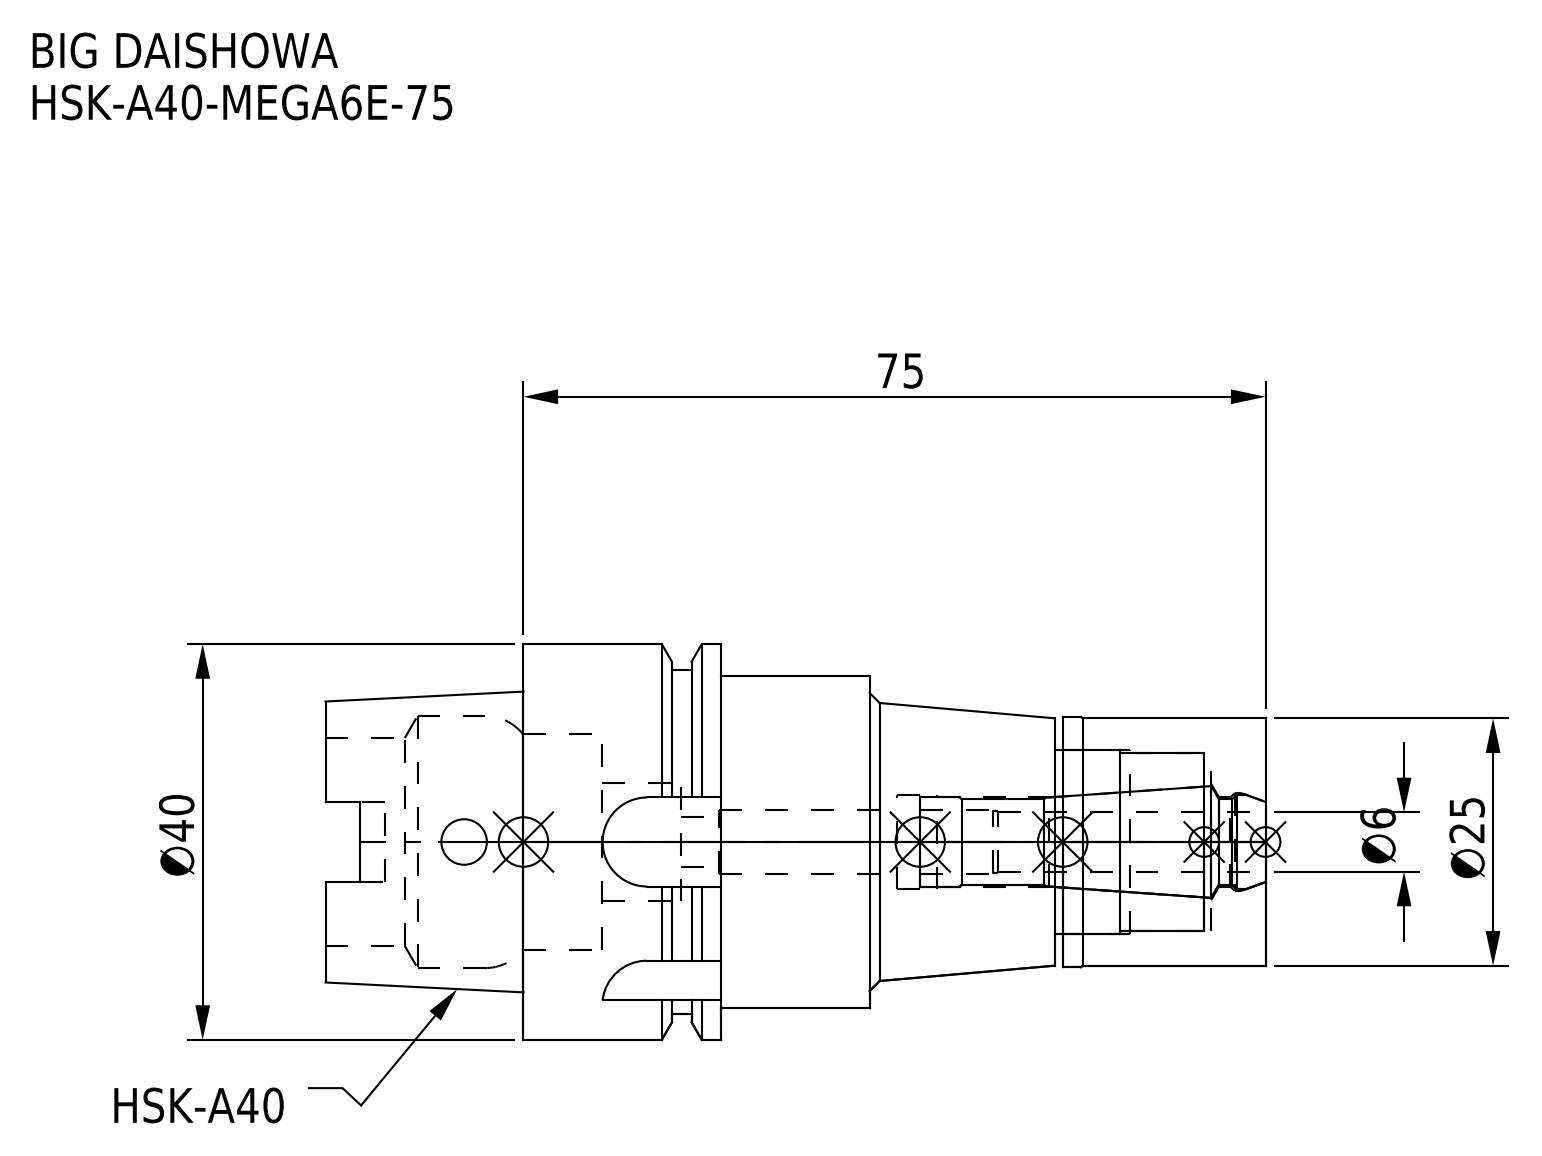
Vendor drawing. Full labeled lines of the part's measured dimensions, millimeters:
Part name (STEP PRODUCT): DXF_TEMP_ASSY_ASM_4_ASM.stp; HSK-A40-MEGA6E-75-060-FreeParts; HA40ME06075-060_ASM.stp; HSK-A40-MEGA6E-75 (+3 more)
STEP written by: SolidWorks 2019 (CONFIG_CONTROL_DESIGN)
Units: millimetres
Bodies: 2 solids, 130 faces (46 planar, 56 cylindrical, 28 other)
Overall size (bounding box): 95 × 40 × 40
Volume: 55 016 mm³ · Surface area: 18 163 mm²
Round holes (diameter × count): ⌀4.6 ×1, ⌀5 ×1, ⌀6.4 ×1, ⌀9 ×1, ⌀9.6 ×1, ⌀9.9 ×1, ⌀12 ×1, ⌀18 ×1, ⌀18.5 ×1, ⌀21 ×1, ⌀21.8 ×1, ⌀25.5 ×1
Round bosses / shafts (diameter × count): ⌀40 ×1, ⌀34.8 ×1, ⌀33.6 ×1, ⌀25.3 ×1, ⌀25 ×1
Partial cylindrical surfaces — rounded edges, fillets, slot ends (radius × count): R1.88 ×4, R4.5 ×4
Main face-to-face distances: 20, 55, 75, 15, 34.5, 40, 54.5, 67.05, 12.05, 7.95
